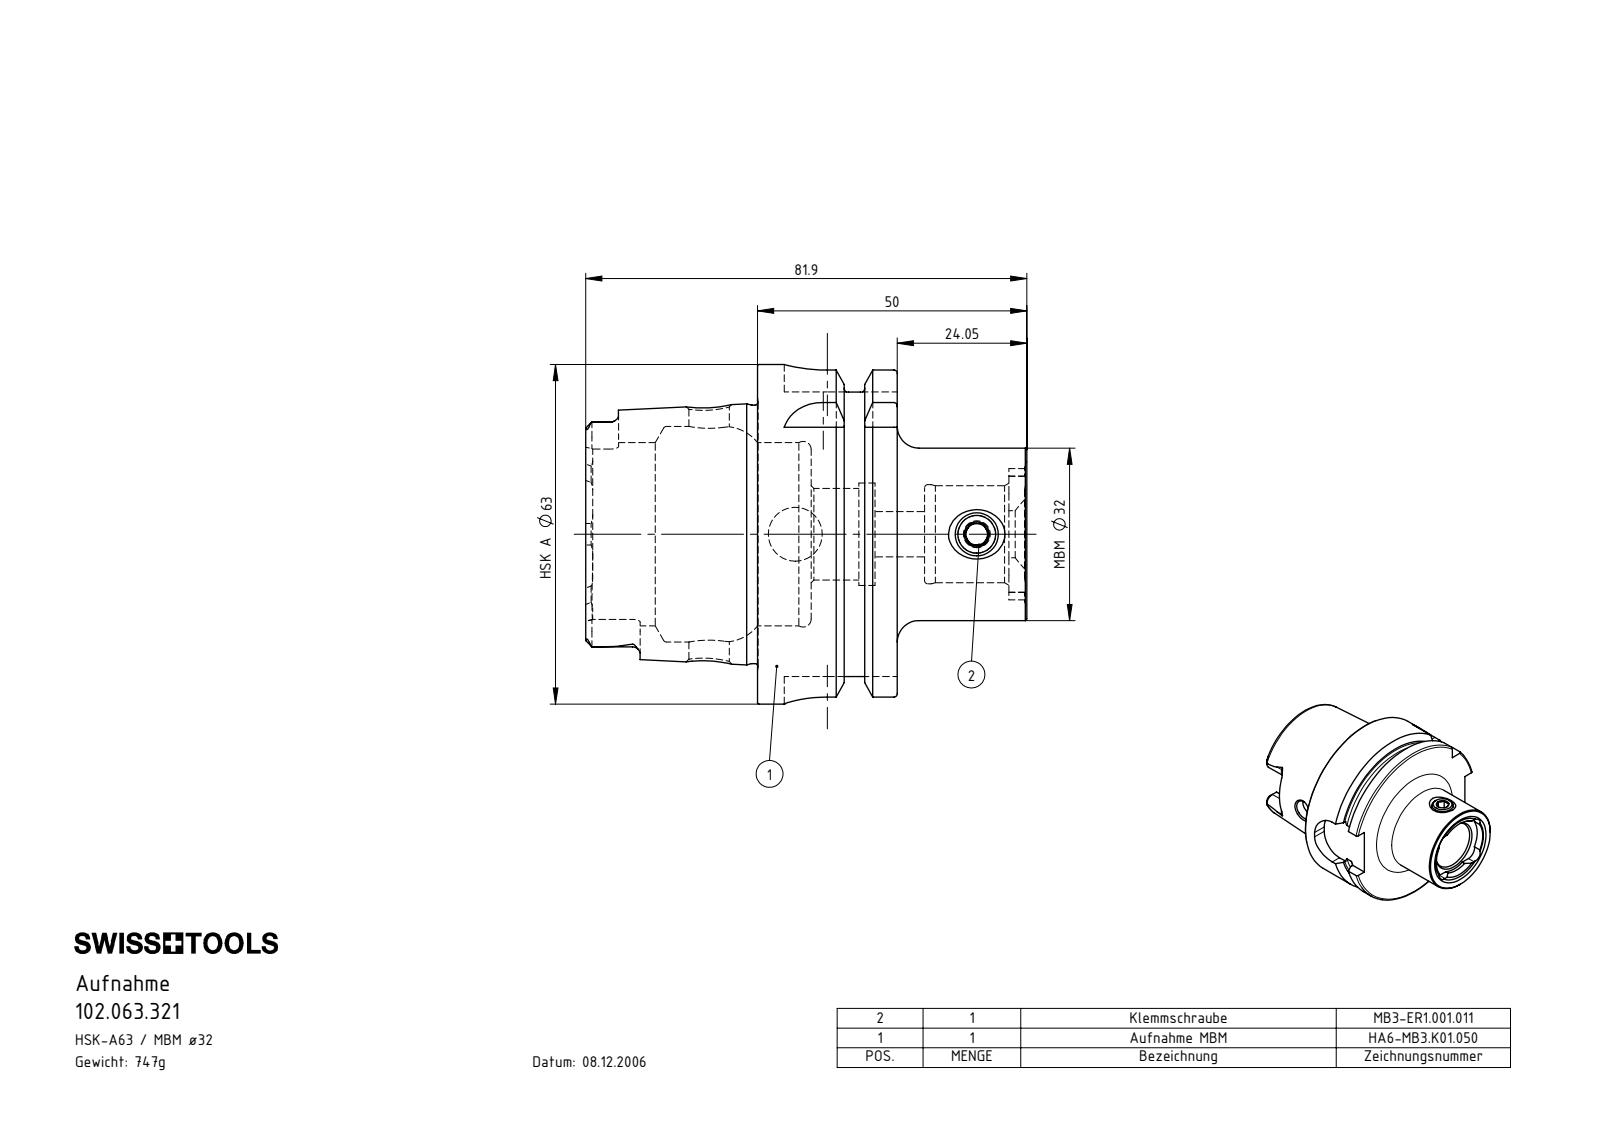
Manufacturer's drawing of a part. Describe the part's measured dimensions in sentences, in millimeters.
The part is named "HA6-MB3.K01.050_A_Fertigbearbeitung; HA6.MB3.K01.050; MB3-ER1.001.011_A". Its 3-D file was written by "SolidWorks 2012 (CONFIG_CONTROL_DESIGN)". It is 2 solids with 225 faces: 64 planar, 64 cylindrical and 97 other. Overall it measures 81.9 by 63 by 63 millimeters. Its volume is 95 204 cubic millimeters and its surface area 26 108 square millimeters. Round holes: 1 of diameter 7, 1 of diameter 7.5, 1 of diameter 8.4, 1 of diameter 10, 1 of diameter 17, 1 of diameter 18, 1 of diameter 18.4, 1 of diameter 19, 1 of diameter 34, 1 of diameter 40. Round bosses or shafts: 1 of diameter 63, 1 of diameter 54.95, 1 of diameter 47.94, 1 of diameter 32, 1 of diameter 8. Partial cylindrical surfaces (rounded edges, fillets, slot ends): 6 of radius 1.4, 4 of radius 2.88, 4 of radius 3.2, 4 of radius 8, 1 of radius 10.5, 1 of radius 12.18. The main face-to-face distances are 25.95, 16, 9.95, 52.8, 31.9, 41.85, 57.85, 21.8, 11.85, 53.7. The hole center spacings are 33.7.
